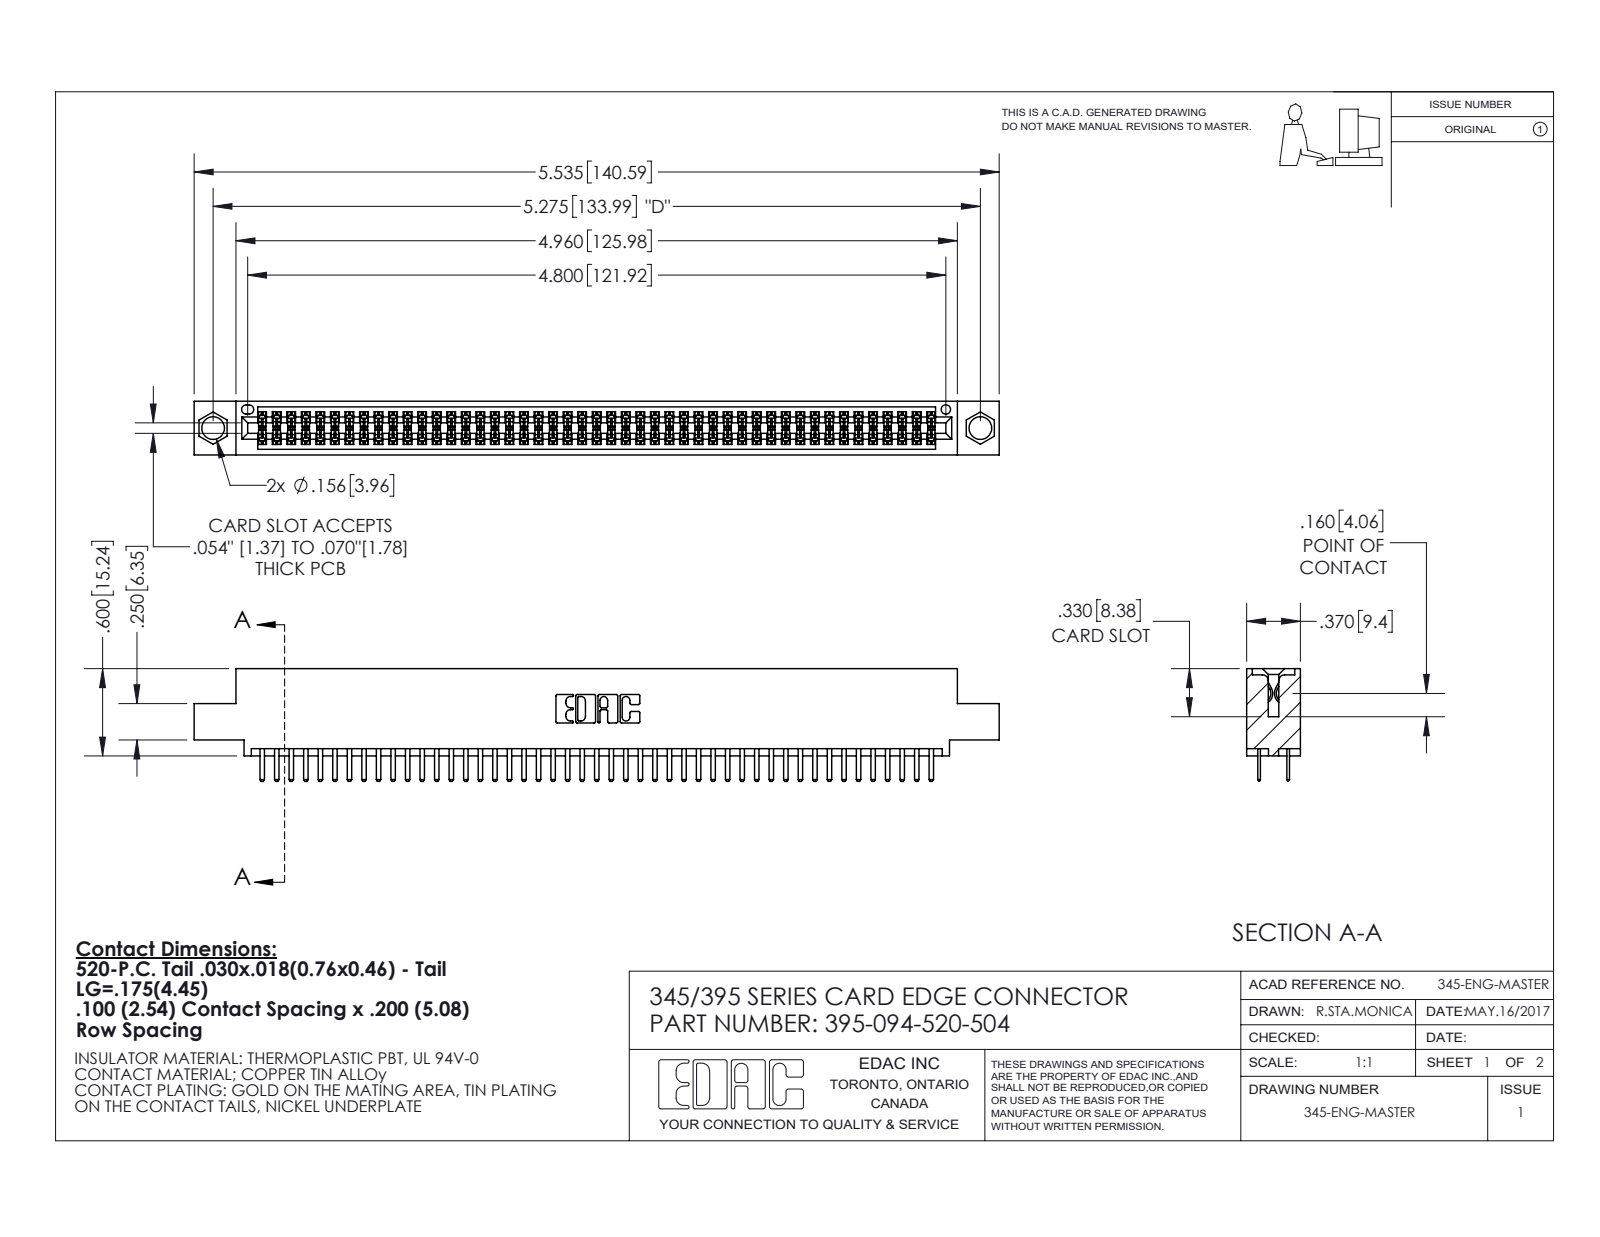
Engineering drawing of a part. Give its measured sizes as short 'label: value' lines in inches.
name: 395-094-520-504; 345 Part_0.110 Offset - 0.156 Dia-TI; 345-292-001_345-293-120
written by: SolidWorks 2020 (CONFIG_CONTROL_DESIGN)
unit: in
bodies: 95 solids, 5220 faces (3388 planar, 1832 cylindrical, 0 other)
size: 5.535 × 0.775 × 0.37
volume: 0.823 in³; area: 30.82 in²
holes: 2× ⌀0.156, 1× ⌀0.064
rounds: 188× R0.006, 98× R0.01, 22× R0.01, 6× R0.007, 6× R0.031, 3× R0.026, 2× R0.014, 2× R0.019
face distances: 0.072, 0.298, 0.2, 0.37, 0.098, 0.272, 0.025, 0.225, 0.022, 0.072
hole spacings: 0.27, 5.039, 5.275
